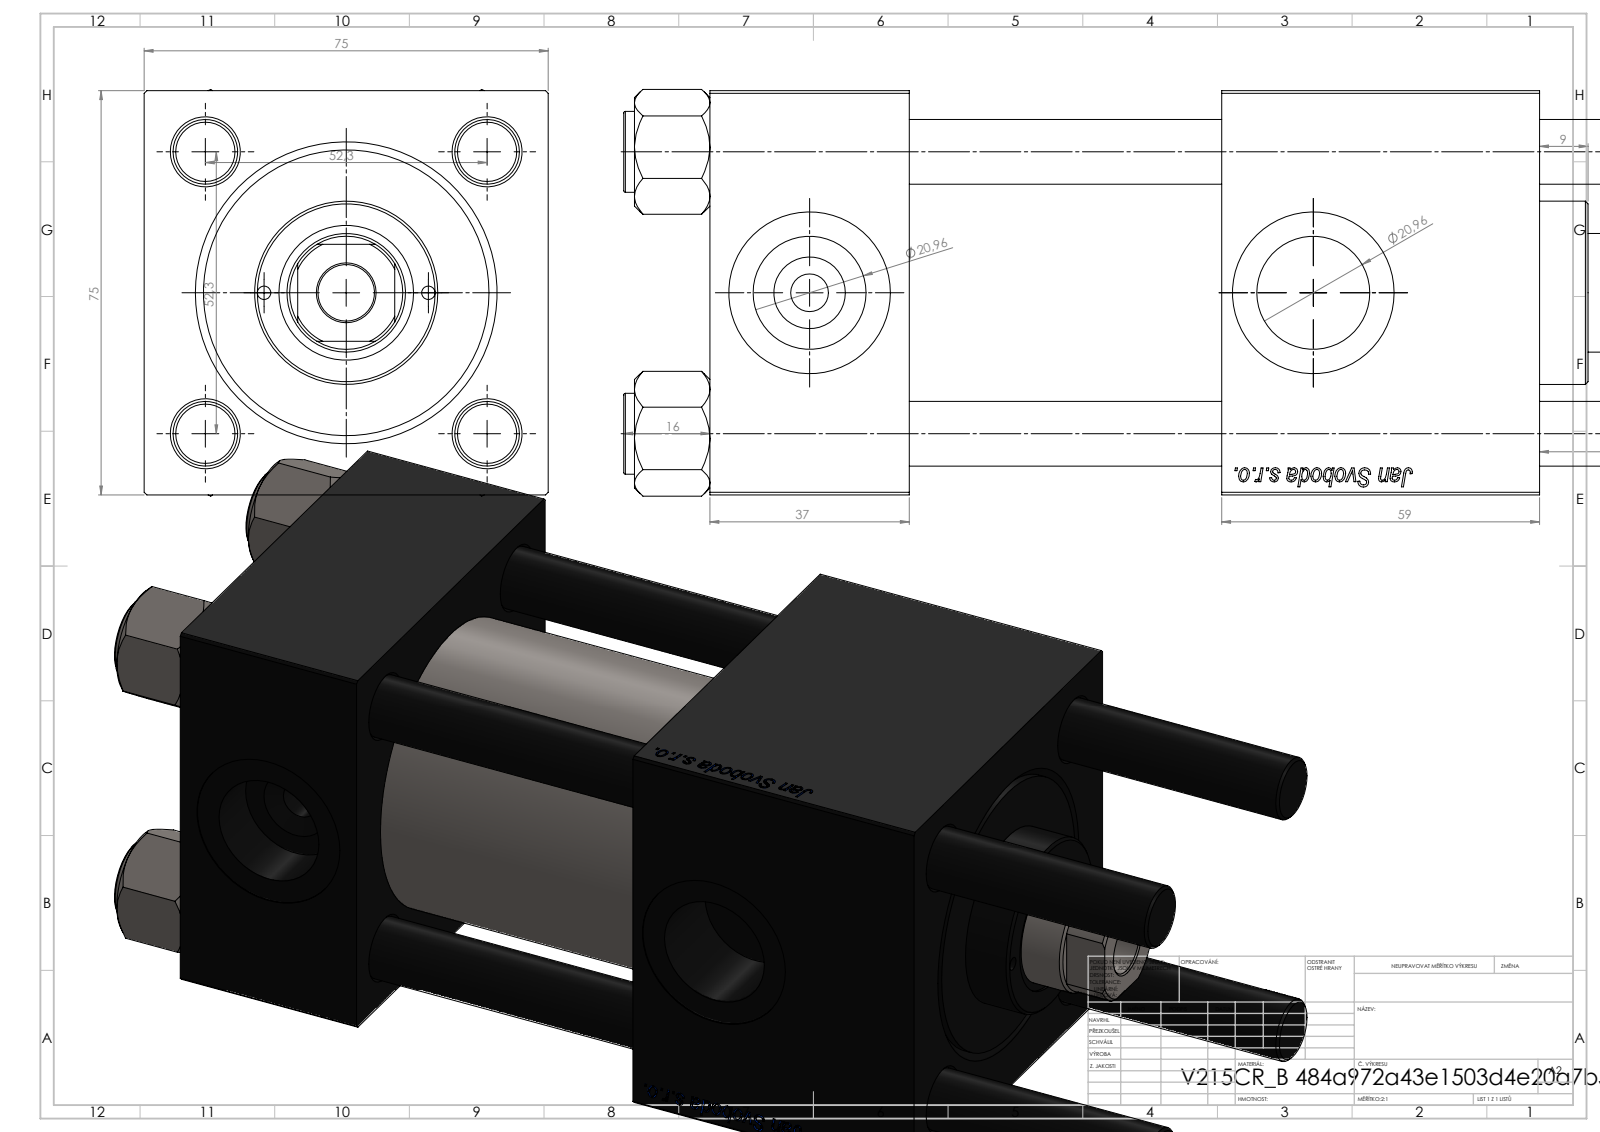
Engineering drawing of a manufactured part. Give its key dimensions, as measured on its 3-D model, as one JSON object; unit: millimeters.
{"part_name": "V215_VC_A; V215CR_VCP_B; NUT_M5_B; V215CR_B-1 (+1 more)", "step_written_by": "SolidWorks 2019 (CONFIG_CONTROL_DESIGN)", "units": "millimeters", "bodies": {"solids": 11, "faces": 1164, "planar": 434, "cylindrical": 82, "other": 648}, "overall_size": [216, 75.45, 75], "volume_mm3": 690011, "surface_area_mm2": 163710, "round_holes": [[12, 4], [2.5, 2], [7, 2], [20.96, 2], [30, 2], [10.5, 1], [22, 1], [25, 1], [41, 1], [50, 1], [53, 1]], "round_bosses_or_shafts": [[15, 4], [56, 1], [34, 1]], "partial_cylinders_radius": [[10.5, 1]], "face_to_face_distances": [75, 37, 154, 117, 95, 58, 59, 125.3, 88.3, 30.3], "hole_center_spacings": [28.33, 36.98, 48.97, 52.3, 15.25, 73.96, 30.5, 93.5]}
